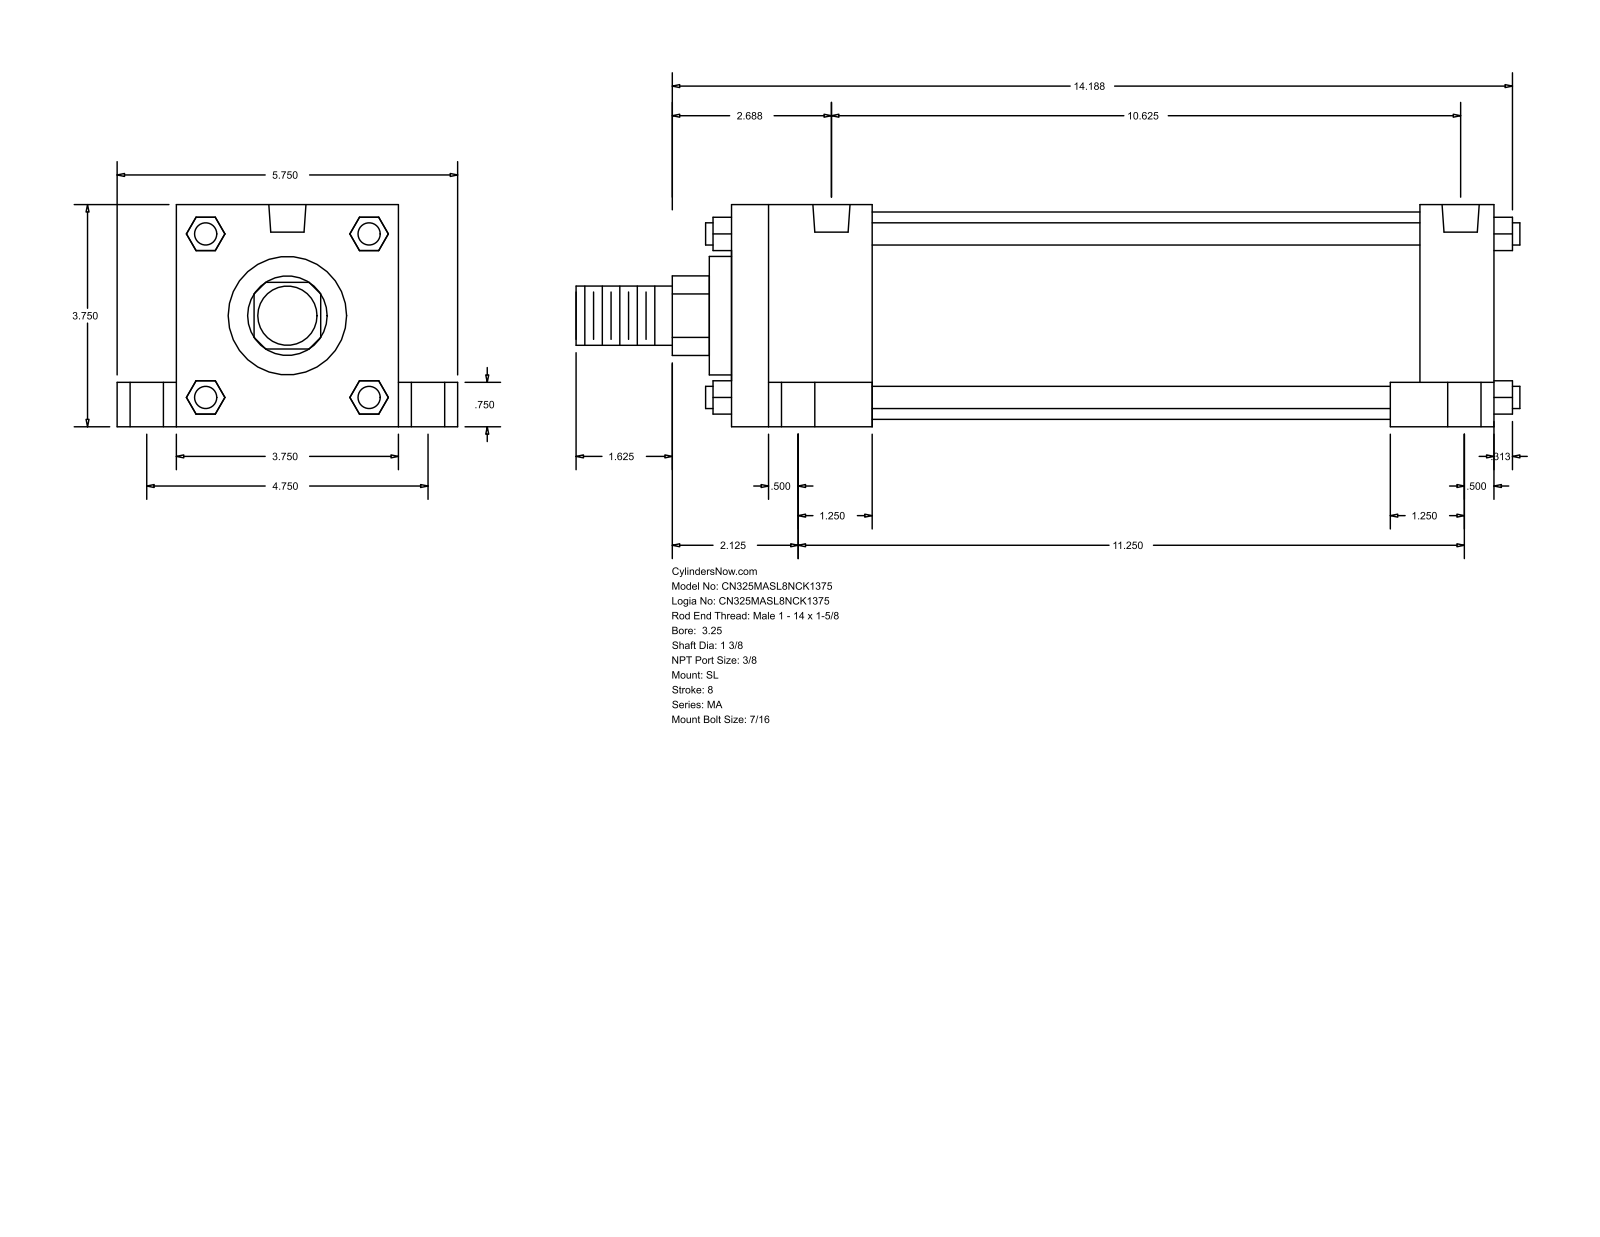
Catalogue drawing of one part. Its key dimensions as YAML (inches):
part_name: "MA_SL__0325_1.375"
step_written_by: "GSSL Pune (CONFIG_CONTROL_DESIGN)"
units: inches
bodies: {solids: 0, faces: 148, planar: 112, cylindrical: 36, other: 0}
overall_size: [15.937, 5.75, 3.75]
round_holes:
  - {diameter: 0.437, count: 4}
  - {diameter: 0.563, count: 4}
  - {diameter: 0.813, count: 4}
  - {diameter: 0.627, count: 2}
round_bosses_or_shafts:
  - {diameter: 0.375, count: 4}
  - {diameter: 3.5, count: 1}
  - {diameter: 2, count: 1}
  - {diameter: 1.375, count: 1}
  - {diameter: 1, count: 1}
partial_cylinders:
  - {radius: 0.672, count: 1}
face_to_face_distances: [3.75, 12.875, 1, 4.75, 11.625, 1.25, 2.375, 9.25, 10.5, 0.75]
hole_center_spacings: [2.376, 2.388, 2.441, 2.491, 4.75, 10.25, 10.765, 10.948]
